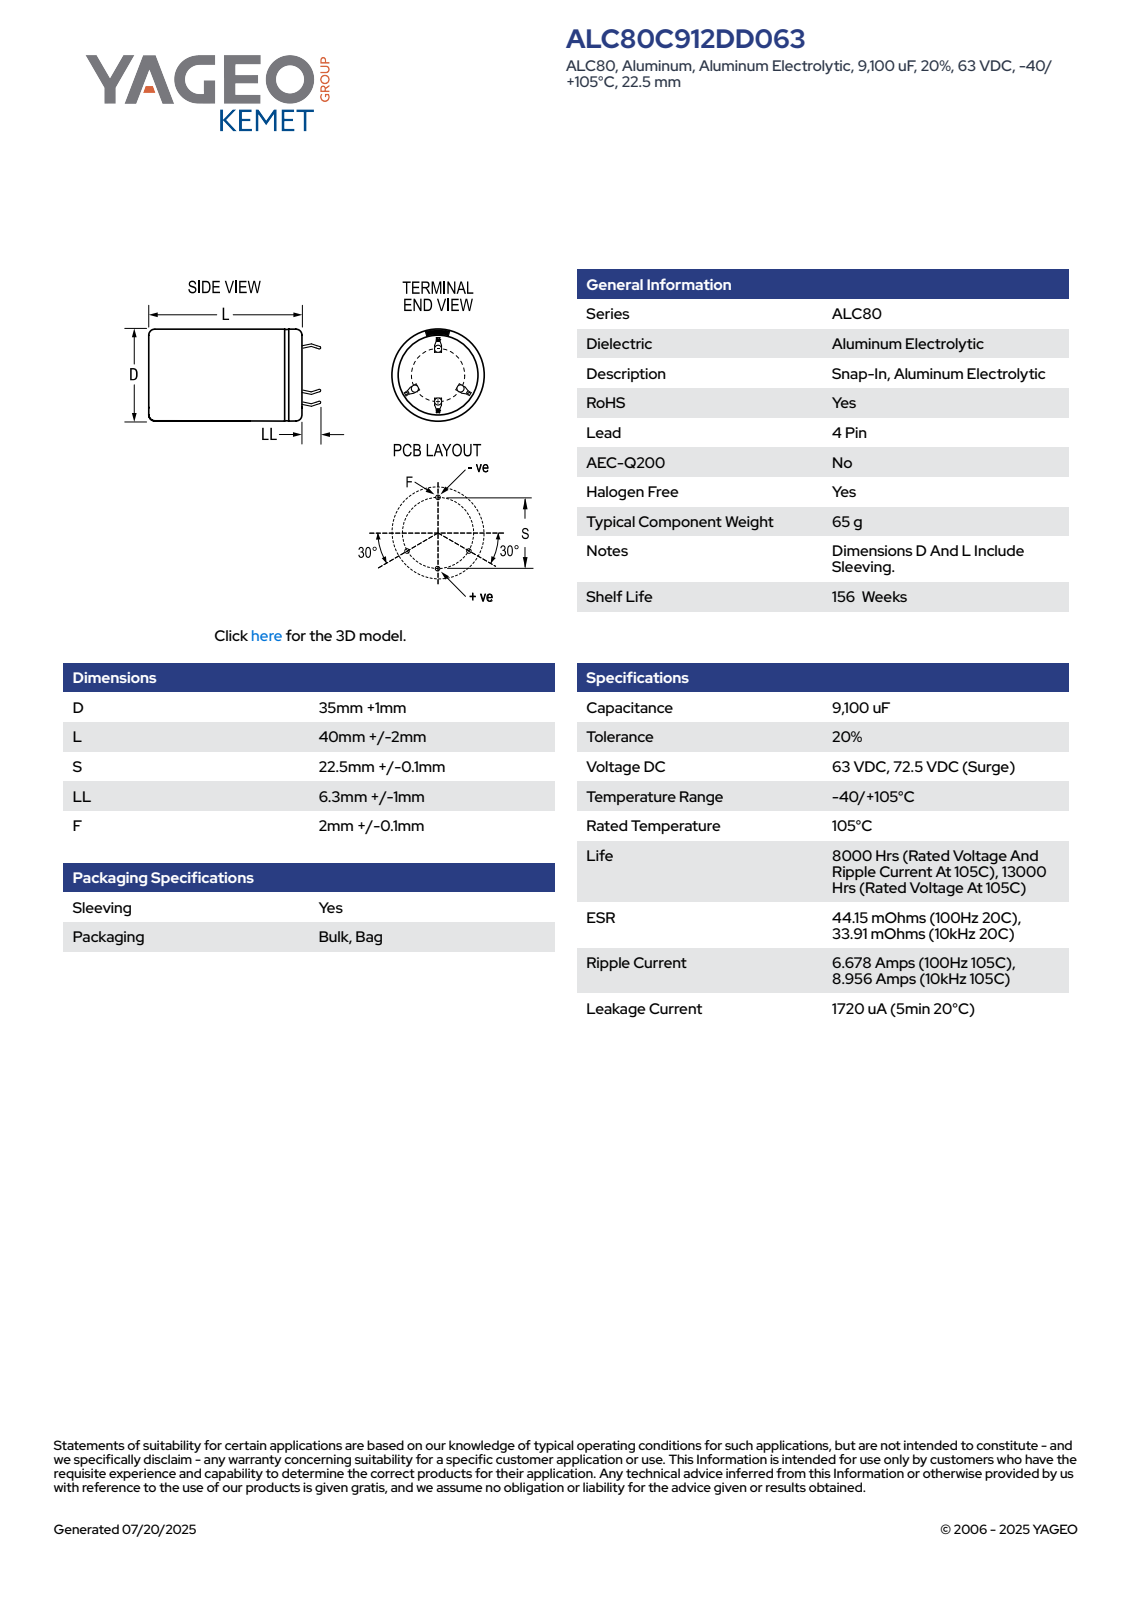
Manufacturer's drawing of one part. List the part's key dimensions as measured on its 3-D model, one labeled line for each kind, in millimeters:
Part name (STEP PRODUCT): CARS_K4P_35X40_D36L42S22.5LL7.3F2.1
STEP written by: SolidWorks 2014 (AUTOMOTIVE_DESIGN)
Units: millimetres
Bodies: 1 solid, 134 faces (80 planar, 15 cylindrical, 39 other)
Overall size (bounding box): 49.29 × 36 × 36
Volume: 42 236 mm³ · Surface area: 6 830 mm²
Round holes (diameter × count): ⌀31.85 ×1
Round bosses / shafts (diameter × count): ⌀36 ×1
Partial cylindrical surfaces — rounded edges, fillets, slot ends (radius × count): R17.99 ×1
Main face-to-face distances: 41.99, 42.49, 0.5, 0.6, 0.75, 1.35, 0.56, 0.57, 2.1, 23.48
